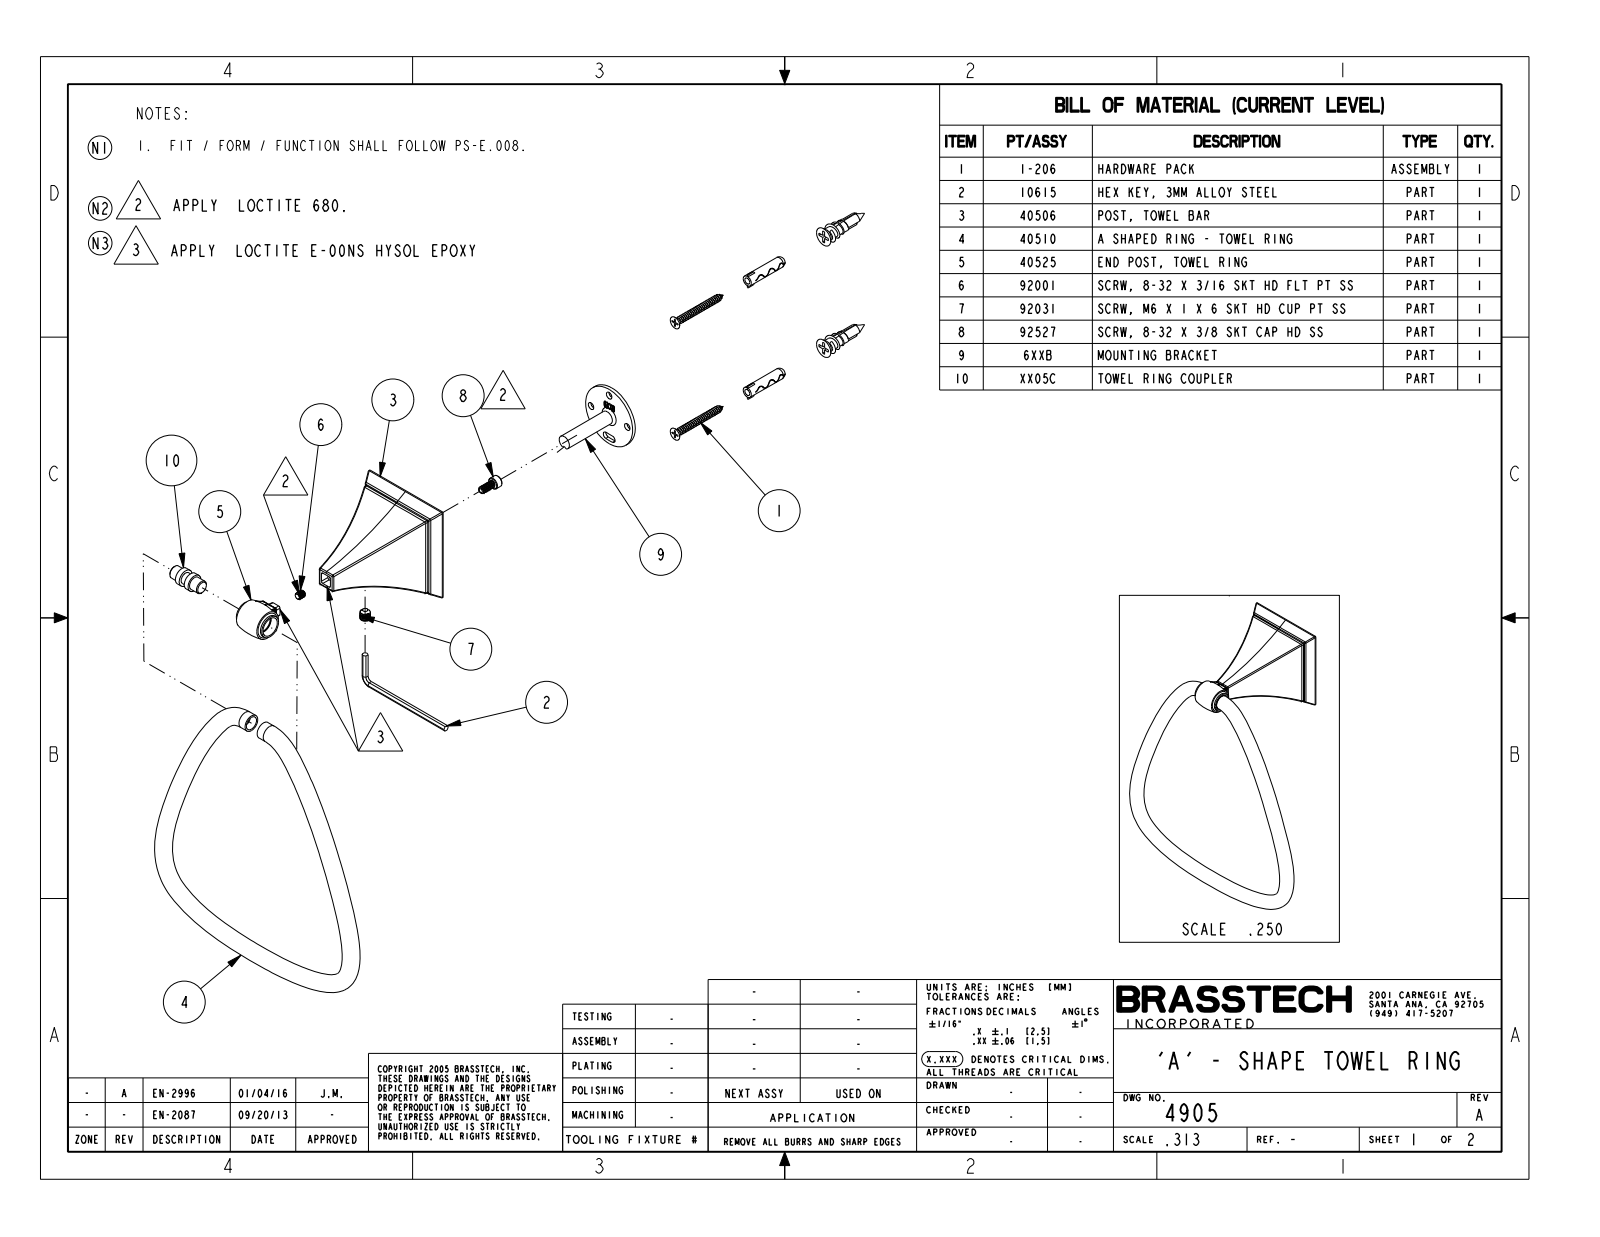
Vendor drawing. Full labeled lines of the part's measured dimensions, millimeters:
Part name (STEP PRODUCT): 40506; 6XXB; 92527; 40525 (+5 more)
STEP written by: PRO/ENGINEER BY PARAMETRIC TECHNOLOGY CORPORATION, 2013150 (CONFIG_CONTROL_DESIGN)
Units: millimetres
Bodies: 8 solids, 721 faces (215 planar, 197 cylindrical, 309 other)
Overall size (bounding box): 190 × 158.3 × 82.8
Volume: 46 740 mm³ · Surface area: 66 520 mm²
Round holes (diameter × count): ⌀4.3 ×3, ⌀3.4 ×1, ⌀5 ×1, ⌀5.1 ×1, ⌀6.4 ×1, ⌀8.2 ×1, ⌀10.3 ×1, ⌀11.3 ×1
Round bosses / shafts (diameter × count): ⌀5.2 ×4, ⌀37.1 ×1, ⌀13.2 ×1, ⌀12.3 ×1, ⌀10.1 ×1, ⌀8 ×1, ⌀7.8 ×1, ⌀7 ×1
Partial cylindrical surfaces — rounded edges, fillets, slot ends (radius × count): R1 ×12, R0.8 ×4, R2 ×4, R5.1 ×4, R2.2 ×2, R2.6 ×2, R4.1 ×2, R4 ×1
Main face-to-face distances: 2, 26.2, 24.1, 3, 58.4, 6, 13, 63.5, 61.4, 37.3
Hole centre spacings: 14.3, 20.2, 28.6
